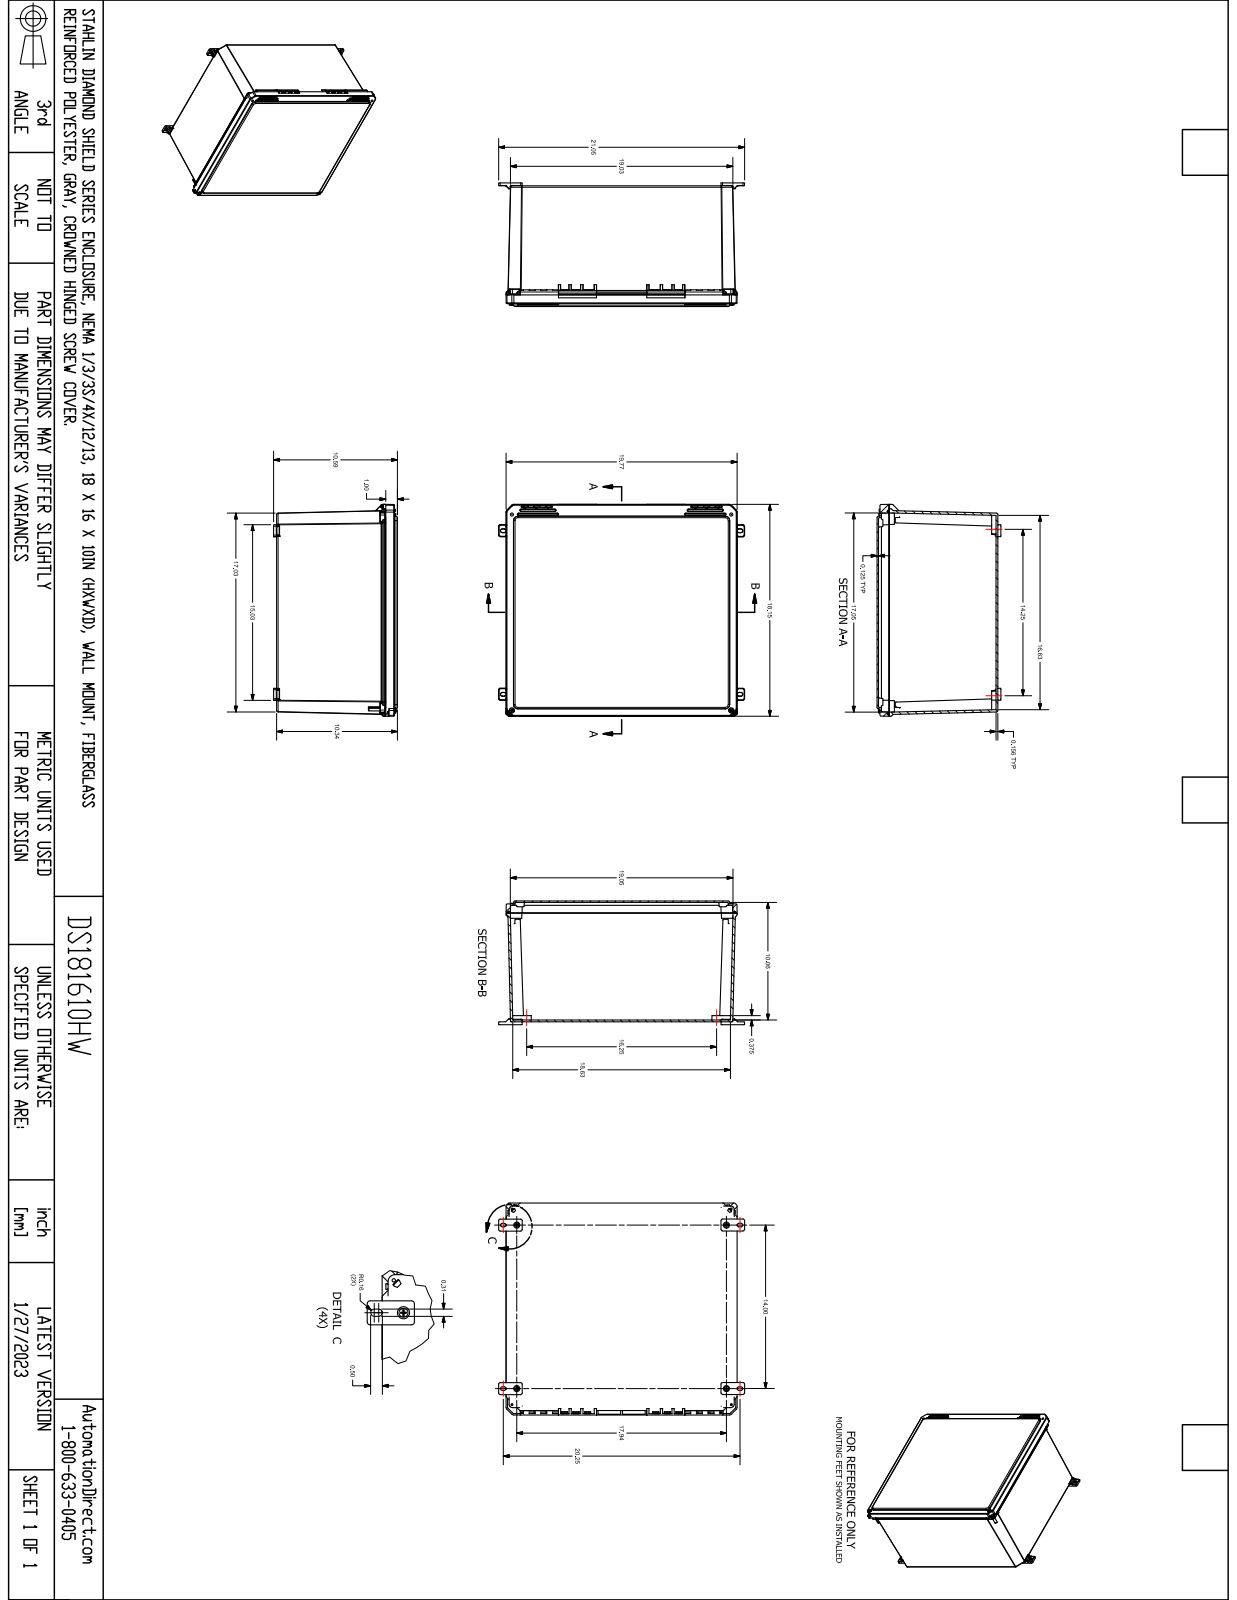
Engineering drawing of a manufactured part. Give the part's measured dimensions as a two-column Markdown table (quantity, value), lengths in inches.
| quantity | value |
| --- | --- |
| part name | FR181610HW |
| STEP written by | SolidWorks 2021 (AUTOMOTIVE_DESIGN) |
| units | inches |
| bodies | 23 solids, 2252 faces (702 planar, 891 cylindrical, 659 other) |
| overall size | 19.778 × 18.16 × 10.911 |
| volume | 259 in³ |
| surface area | 2 945 in² |
| round holes (diameter × count) | 0.152 × 8, 0.159 × 8, 0.156 × 4, 0.252 × 4, 0.253 × 4, 0.137 × 3, 0.15 × 2, 0.219 × 2, 0.227 × 2, 0.313 × 2 |
| round bosses / shafts (diameter × count) | 0.27 × 8, 0.262 × 4, 0.45 × 2, 0.435 × 2, 0.209 × 2, 0.199 × 2, 0.135 × 2 |
| partial cylindrical surfaces (radius × count) | 0.01 × 191, 0.005 × 110, 0.02 × 54, 0.03 × 51, 0.03 × 24, 0.09 × 24, 0.096 × 24, 0.125 × 22 |
| main face-to-face distances | 0.125, 0.156, 10.182, 10.338, 10.213, 10.057, 0.202, 0.199, 0.2, 0.202 |
| hole center spacings | 14.15, 18.409, 1.445, 16.772, 17.556, 22.177, 17.098, 18.77 |
